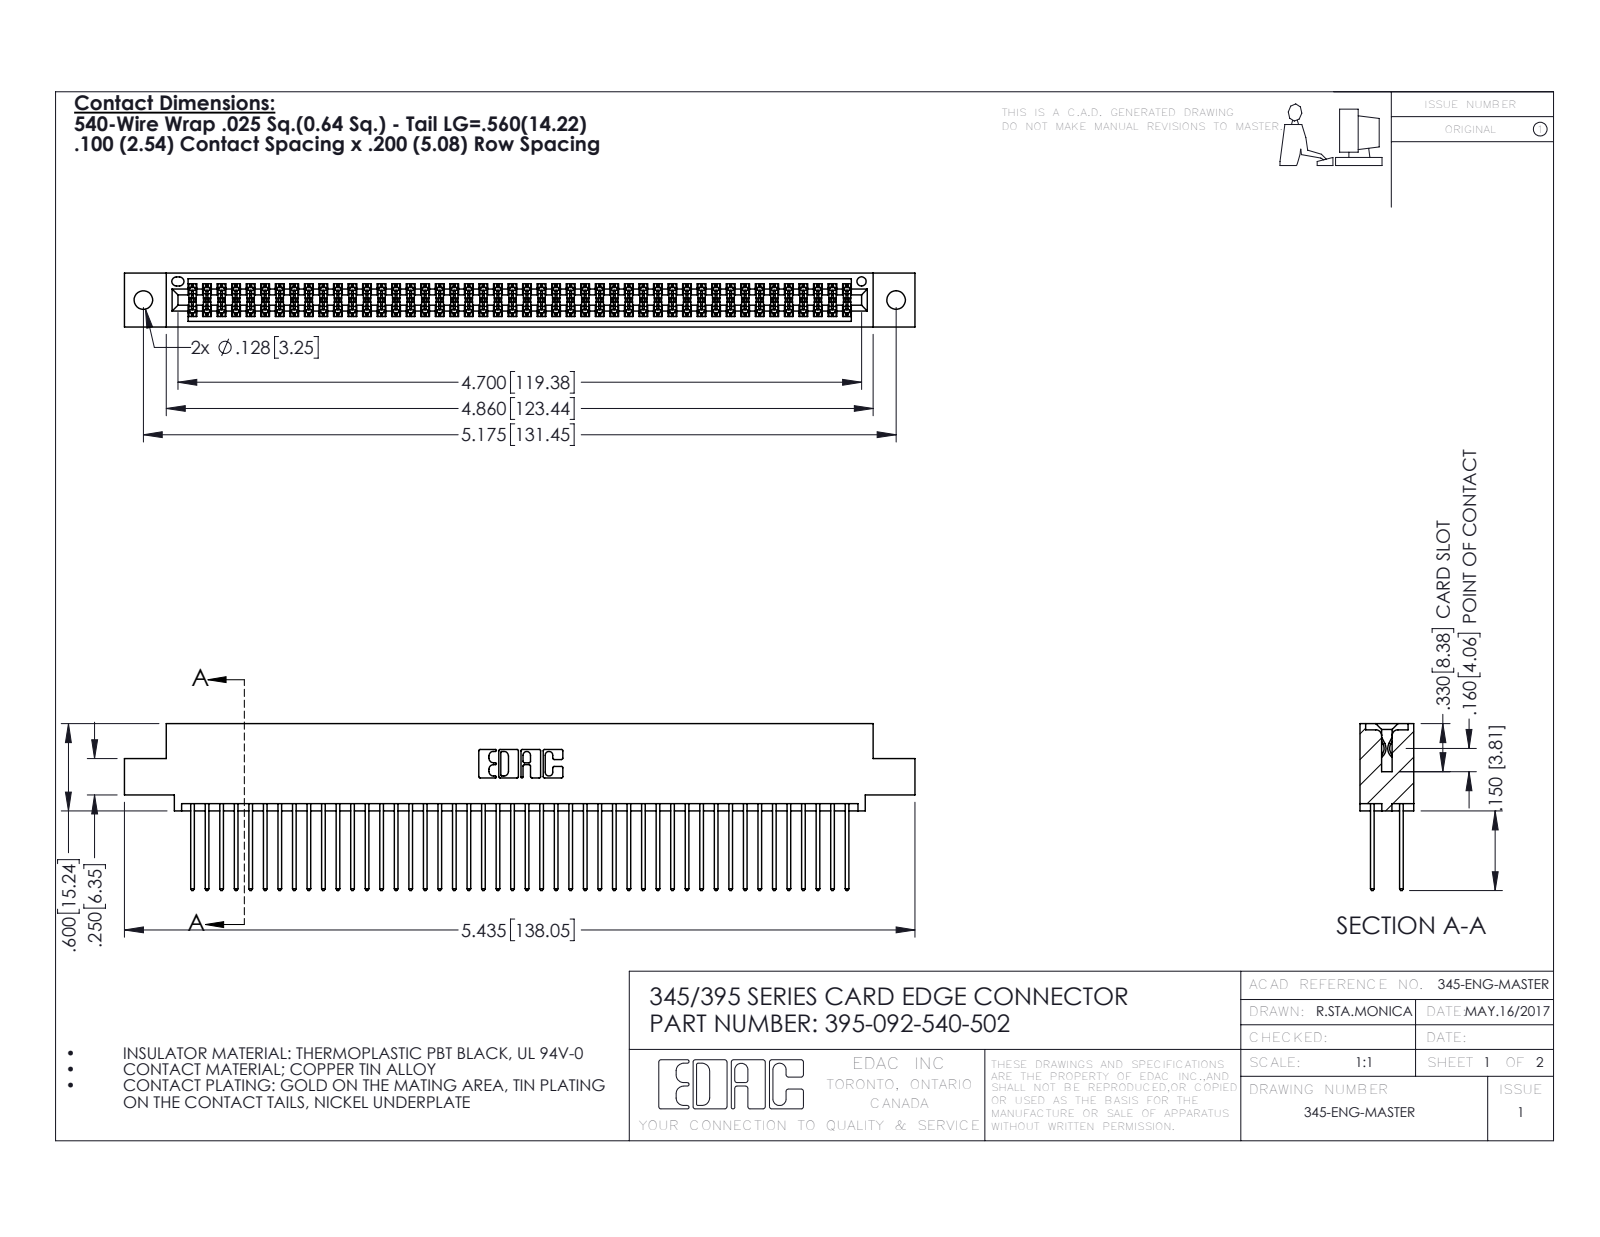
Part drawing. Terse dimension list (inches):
name: 395-092-540-502; 345-292-001_345-293-140; 345 Part_0.110 Offset - 0.128 Dia
written by: SolidWorks 2016 (CONFIG_CONTROL_DESIGN)
unit: in
bodies: 93 solids, 4730 faces (3120 planar, 1610 cylindrical, 0 other)
size: 5.435 × 1.147 × 0.37
volume: 0.835 in³; area: 33.71 in²
holes: 2× ⌀0.128, 1× ⌀0.064
rounds: 138× R0.006, 92× R0.01, 22× R0.01, 6× R0.007, 6× R0.031, 3× R0.026, 2× R0.014, 2× R0.019
face distances: 0.298, 0.072, 0.2, 0.098, 0.272, 0.025, 0.37, 0.225, 0.175, 0.149
hole spacings: 0.27, 4.939, 5.175
